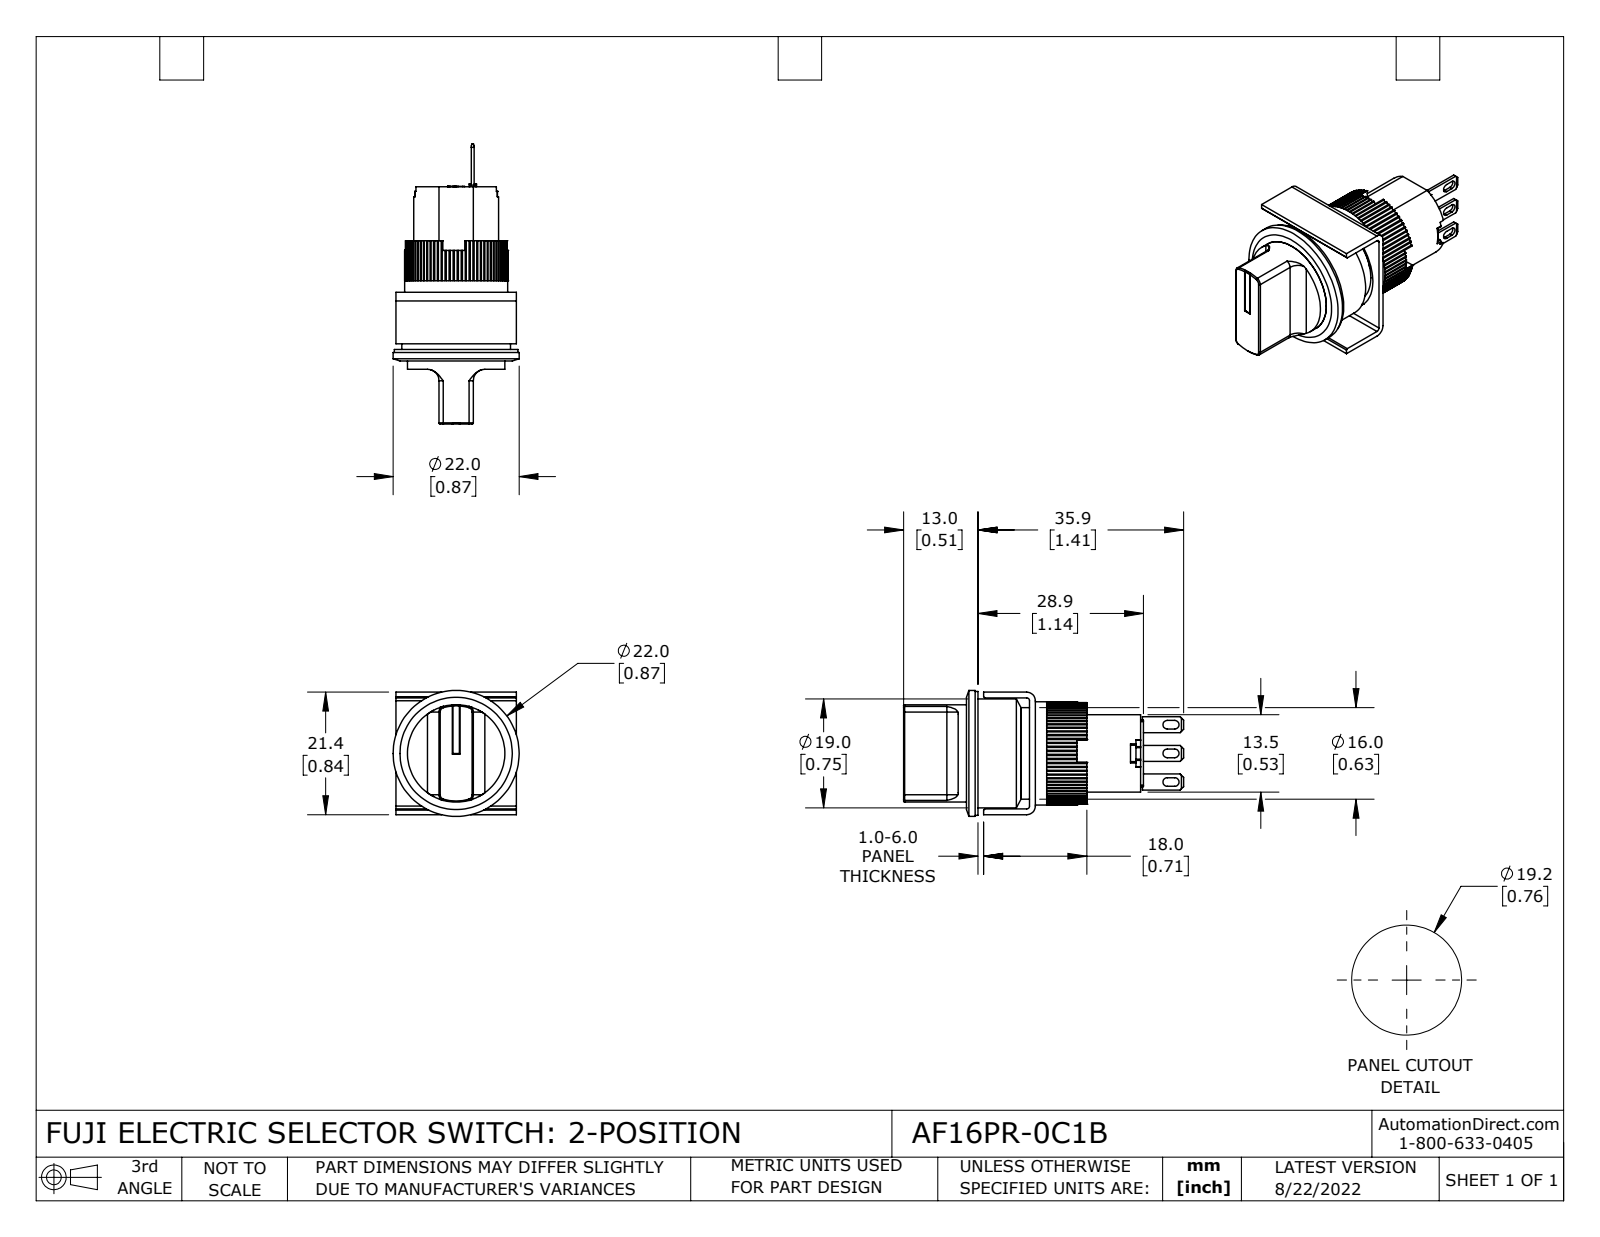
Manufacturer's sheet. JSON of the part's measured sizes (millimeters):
{"part_name": "AF16PR-0C1B", "step_written_by": "SolidWorks 2021 (CONFIG_CONTROL_DESIGN)", "units": "millimeters", "bodies": {"solids": 9, "faces": 638, "planar": 443, "cylindrical": 180, "other": 15}, "overall_size": [48.9, 22, 22], "volume_mm3": 8050, "surface_area_mm2": 6568, "round_holes": [[1, 1], [17, 1], [18, 1], [19, 1]], "round_bosses_or_shafts": [[22, 1], [21.6, 1], [16, 1], [14.8, 1]], "partial_cylinders_radius": [[0.3, 80], [0.2, 14], [0.8, 6], [1, 4], [0.5, 2], [1.5, 2], [2, 2], [8.4, 1]], "face_to_face_distances": [9.5, 1, 1.5, 20.4, 19.4, 11, 5.9, 3.6, 2.9, 3.9]}
